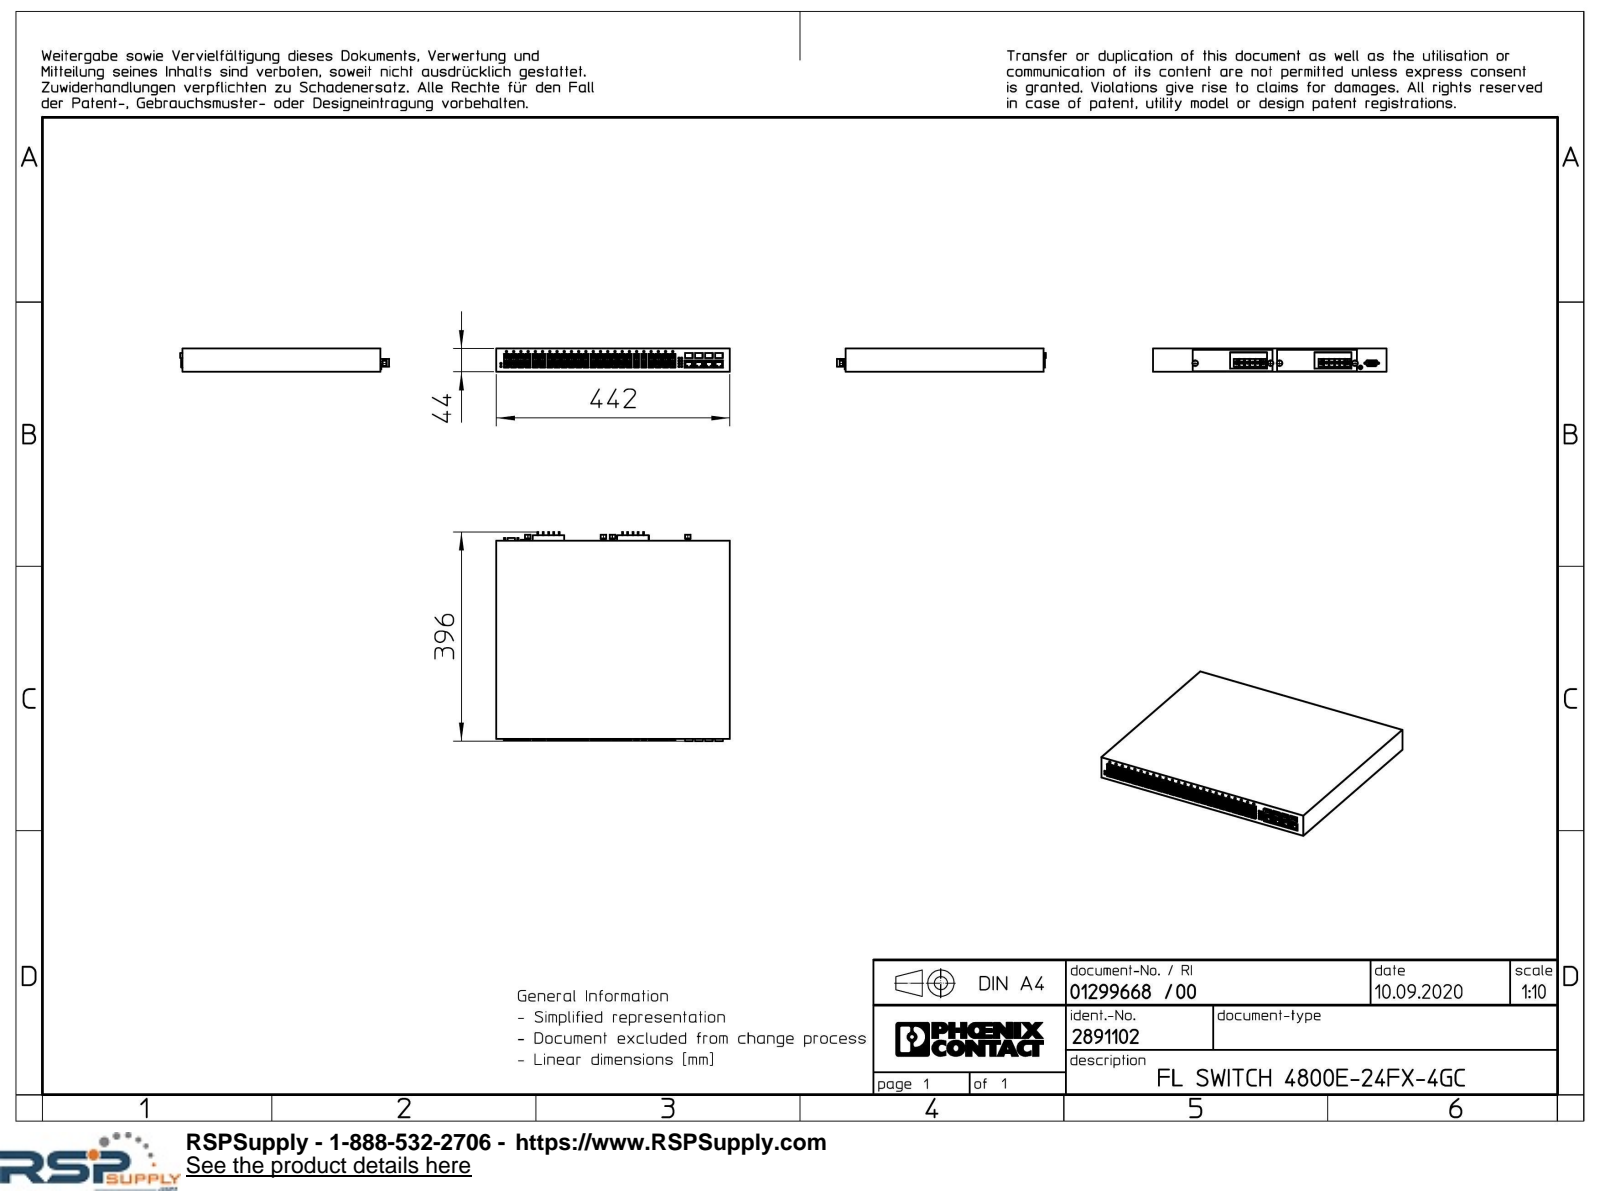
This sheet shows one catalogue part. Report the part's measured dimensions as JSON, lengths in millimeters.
{"part_name": "FL_SWITCH_4808E_24FX_..._4GC-select", "step_written_by": "Creo Elements/Direct Modeling 20.1A 29-Sep-2018 (C) Parametric Technology GmbH (AUTOMOTIVE_DESIGN)", "units": "millimeters", "bodies": {"solids": 1, "faces": 1141, "planar": 797, "cylindrical": 344, "other": 0}, "overall_size": [442, 395.68, 44], "volume_mm3": 7289000, "surface_area_mm2": 451506, "round_holes": [[4, 48], [3.2, 36], [1, 9], [4.5, 8], [7, 4]], "round_bosses_or_shafts": [[5, 48], [6, 8], [10.5, 4], [3, 2], [7, 1]], "partial_cylinders_radius": [[1, 4], [2.5, 4]], "face_to_face_distances": [44, 442, 374.9, 375, 13.7, 10.7, 12.7, 367.51, 367.41, 7.49], "hole_center_spacings": [10, 3.16, 20, 2.77, 30, 160, 150, 170]}
